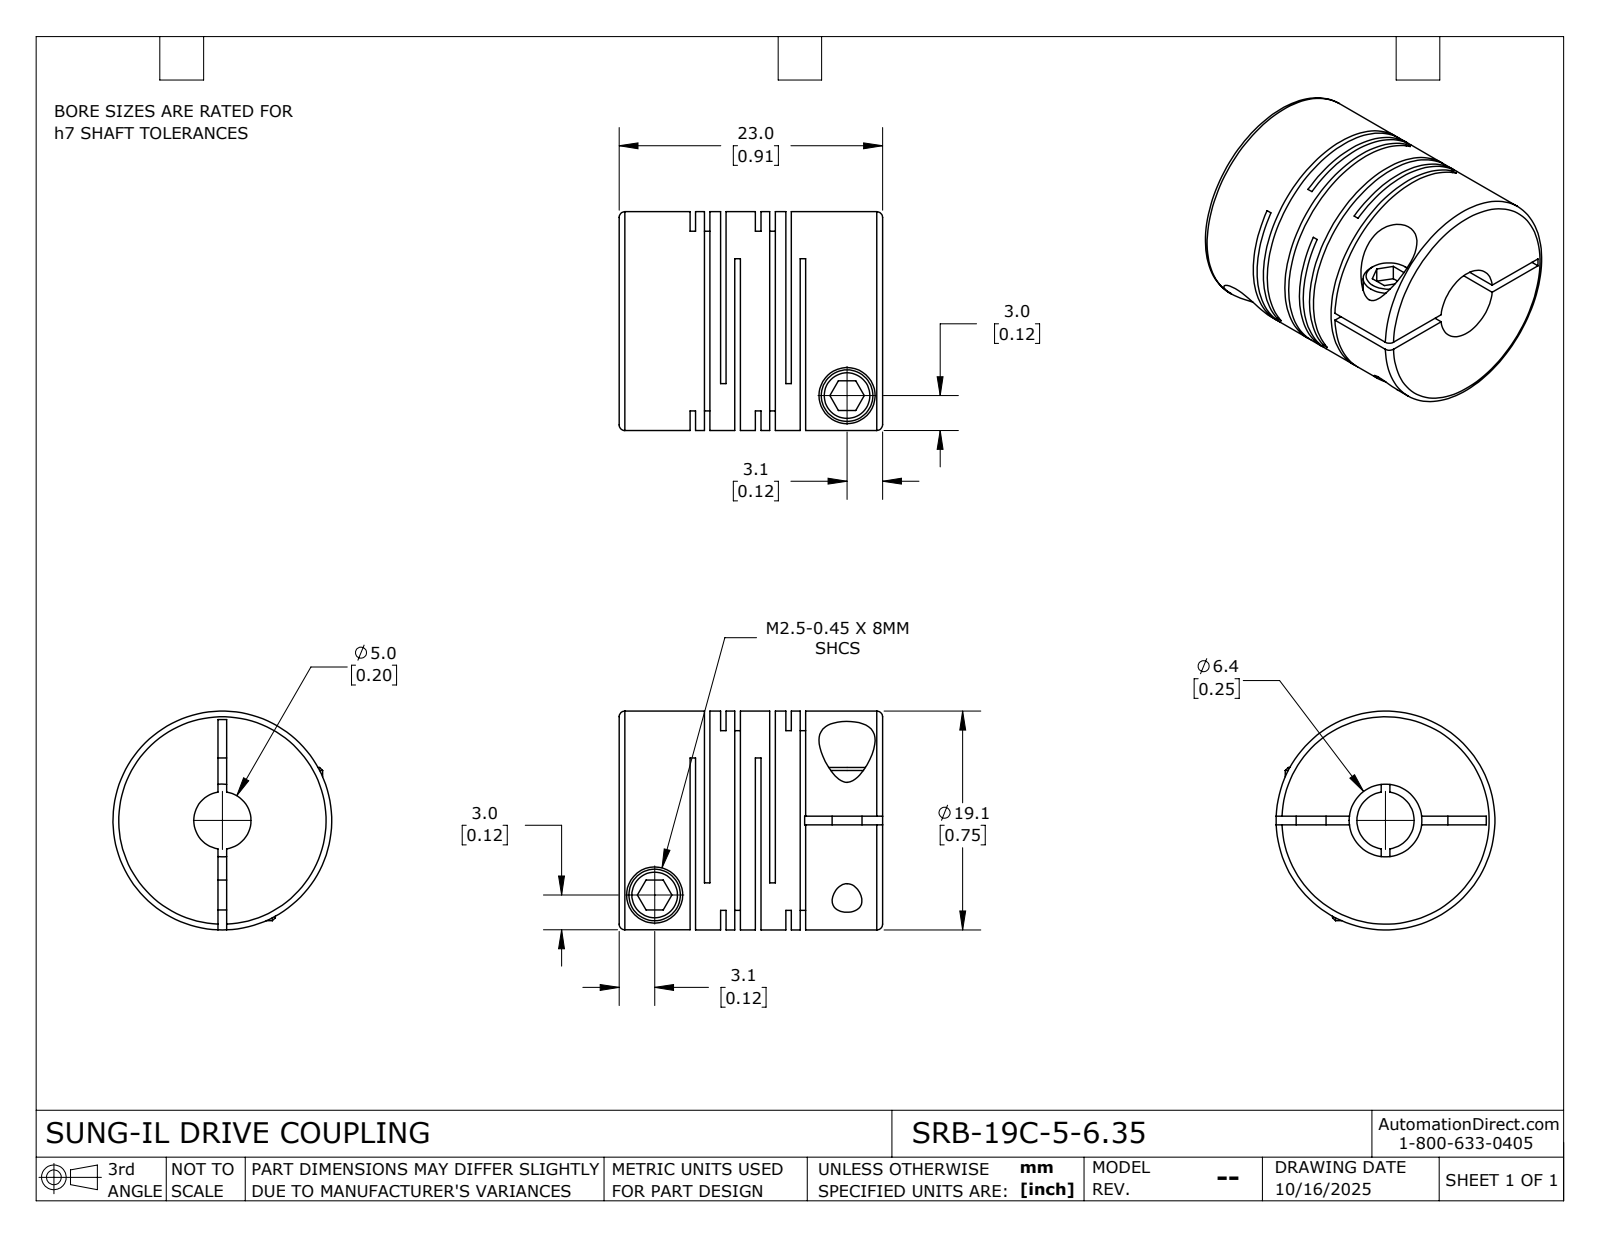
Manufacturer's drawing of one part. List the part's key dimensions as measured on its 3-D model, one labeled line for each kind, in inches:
Part name (STEP PRODUCT): SRB-19C-5-6.35
STEP written by: SolidWorks 2024 (CONFIG_CONTROL_DESIGN)
Units: inches
Bodies: 1 solid, 115 faces (60 planar, 42 cylindrical, 13 other)
Overall size (bounding box): 0.906 × 0.752 × 0.752
Volume: 0.298 in³ · Surface area: 9.267 in²
Round holes (diameter × count): ⌀0.102 ×2, ⌀0.193 ×2, ⌀0.197 ×1, ⌀0.25 ×1
Round bosses / shafts (diameter × count): ⌀0.177 ×2, ⌀0.752 ×1
Main face-to-face distances: 0.104, 0.019, 0.049, 0.224, 0.085, 0.12, 0.206, 0.03, 0.175, 0.055
